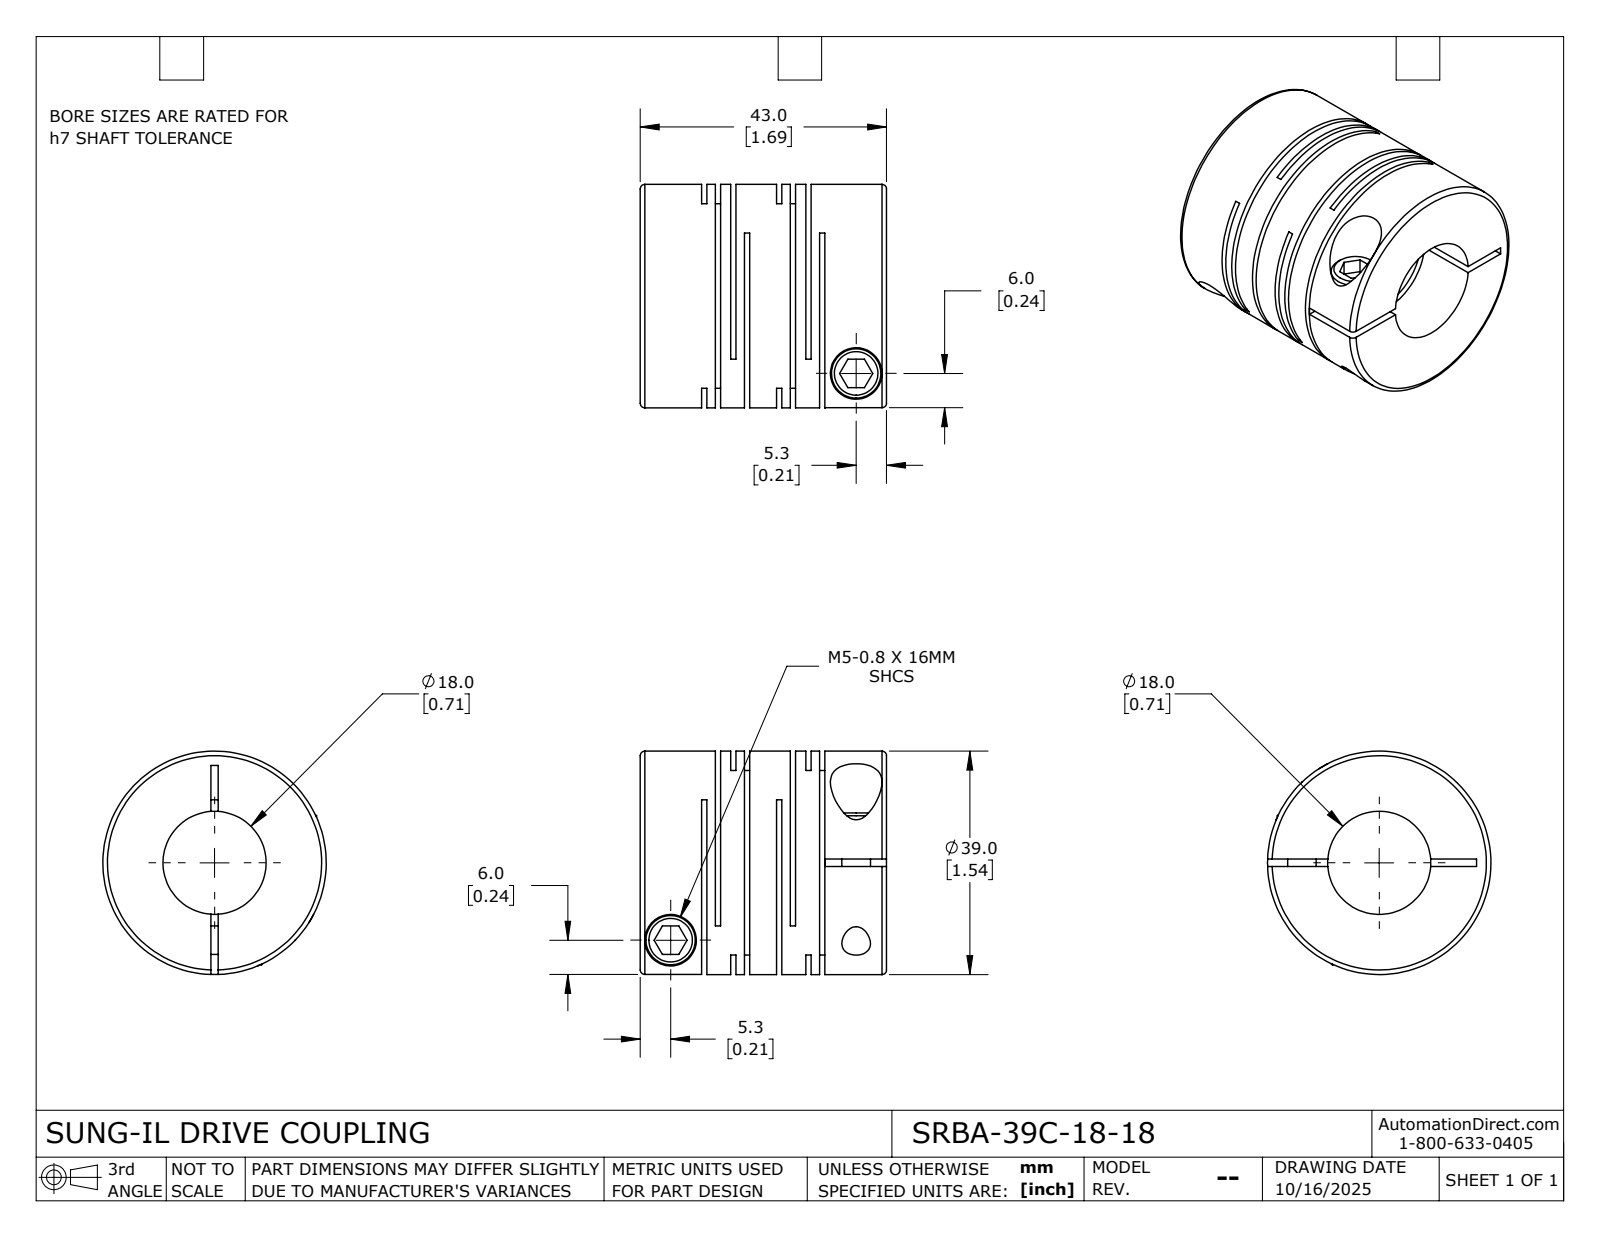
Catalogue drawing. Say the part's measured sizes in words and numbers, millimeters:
The part is named "SRBA-39C-18-18". Its 3-D file was written by "SolidWorks 2024 (CONFIG_CONTROL_DESIGN)". It is 1 solid with 115 faces: 60 planar, 42 cylindrical and 13 other. Overall it measures 43 by 39 by 39 millimeters. Its volume is 33 515 cubic millimeters and its surface area 22 128 square millimeters. Round holes: 2 of diameter 5, 2 of diameter 9, 1 of diameter 18. Round bosses or shafts: 2 of diameter 8.6, 1 of diameter 39. The main face-to-face distances are 13.1, 0.92, 2.4, 5.1, 10.7, 14.02, 18.2, 12.18, 1.48, 4.18.
